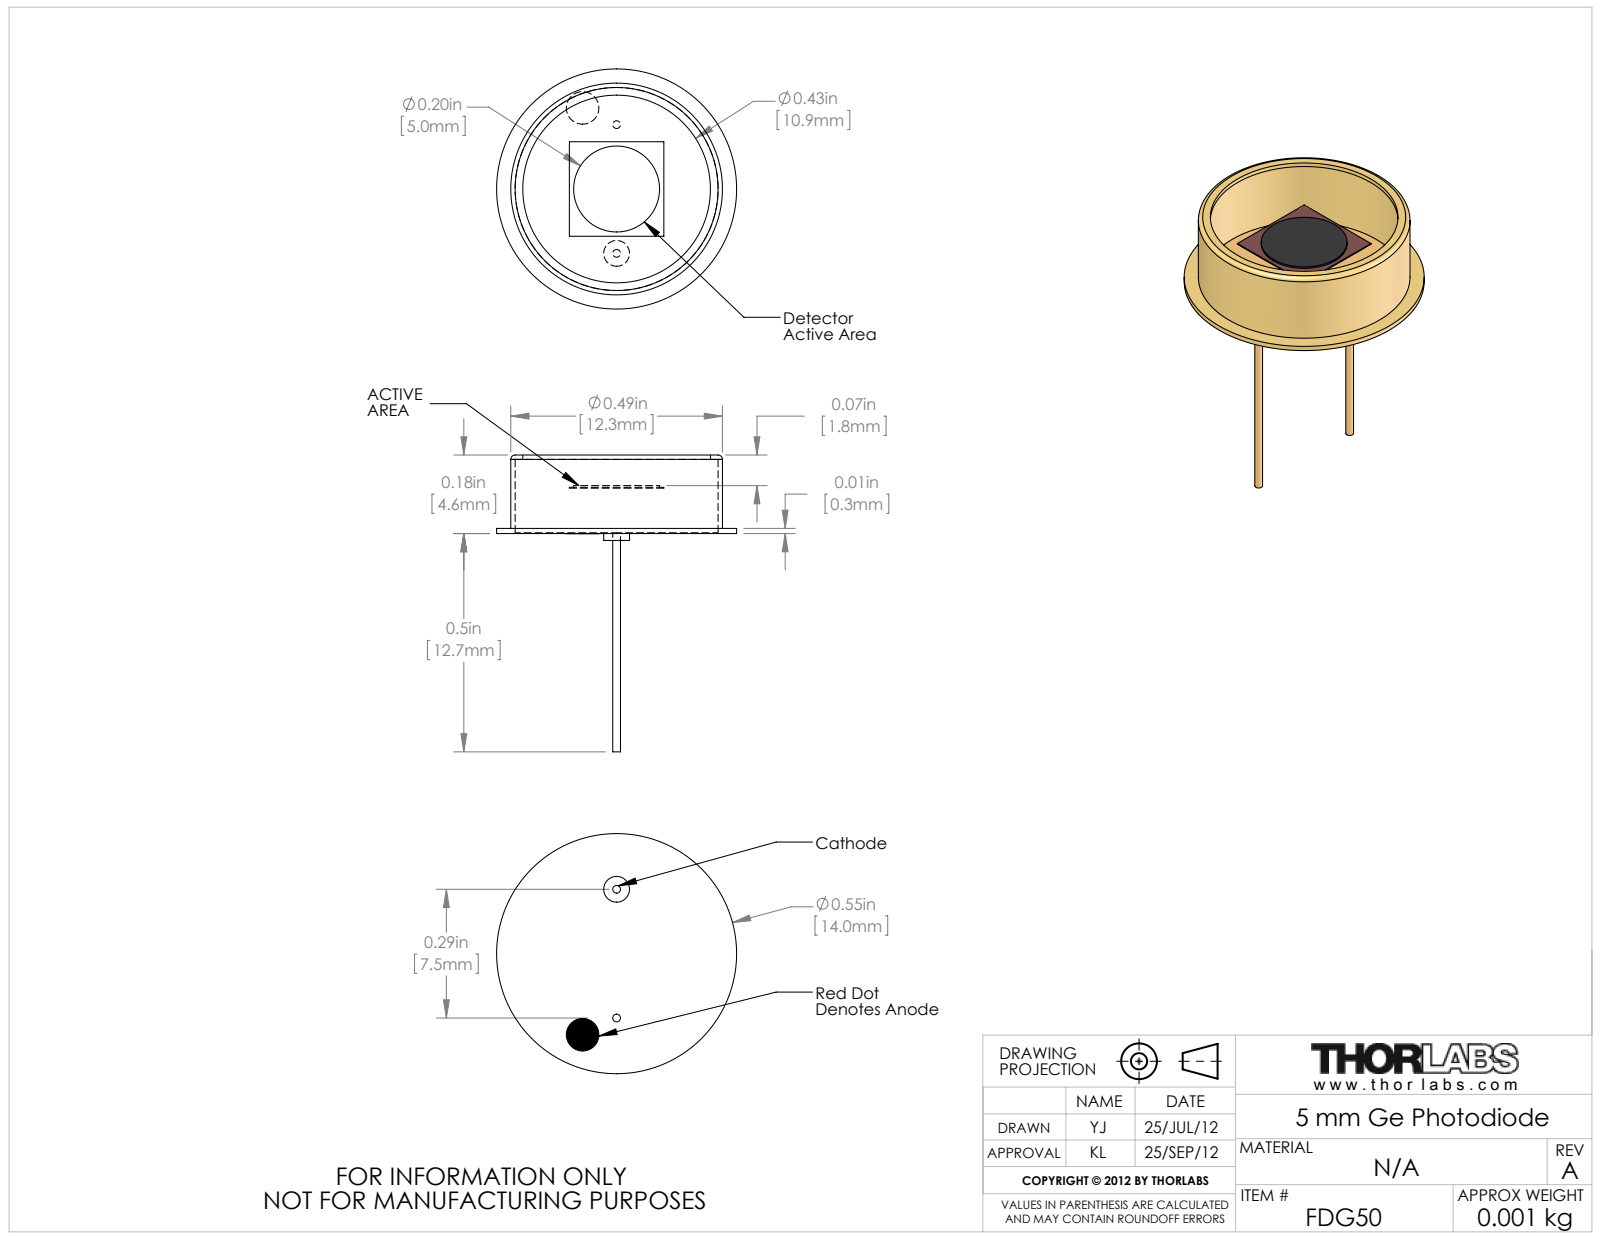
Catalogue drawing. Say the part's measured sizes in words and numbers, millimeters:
The part is named "24704-E0W". Its 3-D file was written by "SolidWorks 2012 (AUTOMOTIVE_DESIGN)". It is 2 solids with 36 faces: 16 planar, 18 cylindrical and 2 other. Overall it measures 17.27 by 13.97 by 13.97 millimeters. Its volume is 128 cubic millimeters and its surface area 767 square millimeters. Round holes: 1 of diameter 10.92, 1 of diameter 11.81. Round bosses or shafts: 2 of diameter 0.45, 1 of diameter 13.97, 1 of diameter 12.32, 1 of diameter 5, 1 of diameter 1.89, 1 of diameter 1.5. The main face-to-face distances are 0.45, 0.7, 3.87, 2.64, 2.19, 1.94, 2.79, 2.34, 2.09, 4.32.
